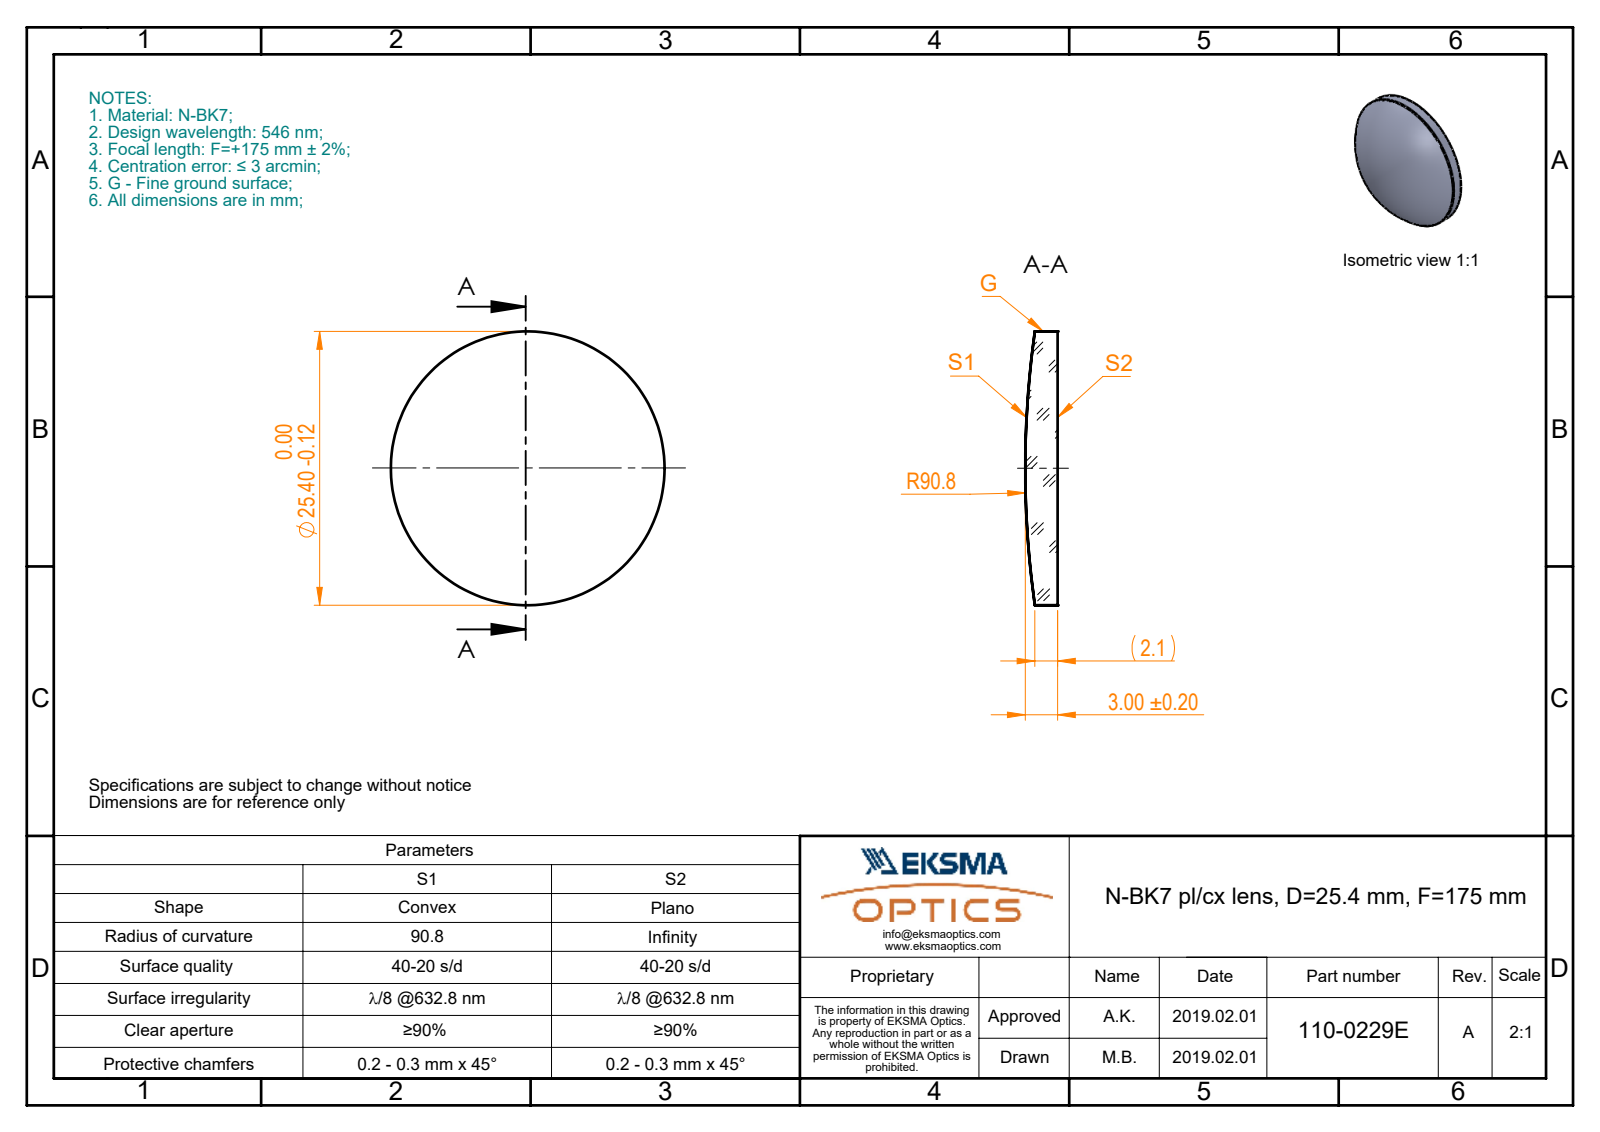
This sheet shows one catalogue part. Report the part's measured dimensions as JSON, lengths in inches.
{"part_name": "110-0229E BK7 pl-cx 25.4 F175", "step_written_by": "SolidWorks 2017 (CONFIG_CONTROL_DESIGN)", "units": "inches", "bodies": {"solids": 1, "faces": 5, "planar": 1, "cylindrical": 2, "other": 2}, "overall_size": [1, 1, 0.118], "volume_in3": 0.079, "surface_area_in2": 1.835, "round_bosses_or_shafts": [[1, 1]]}
